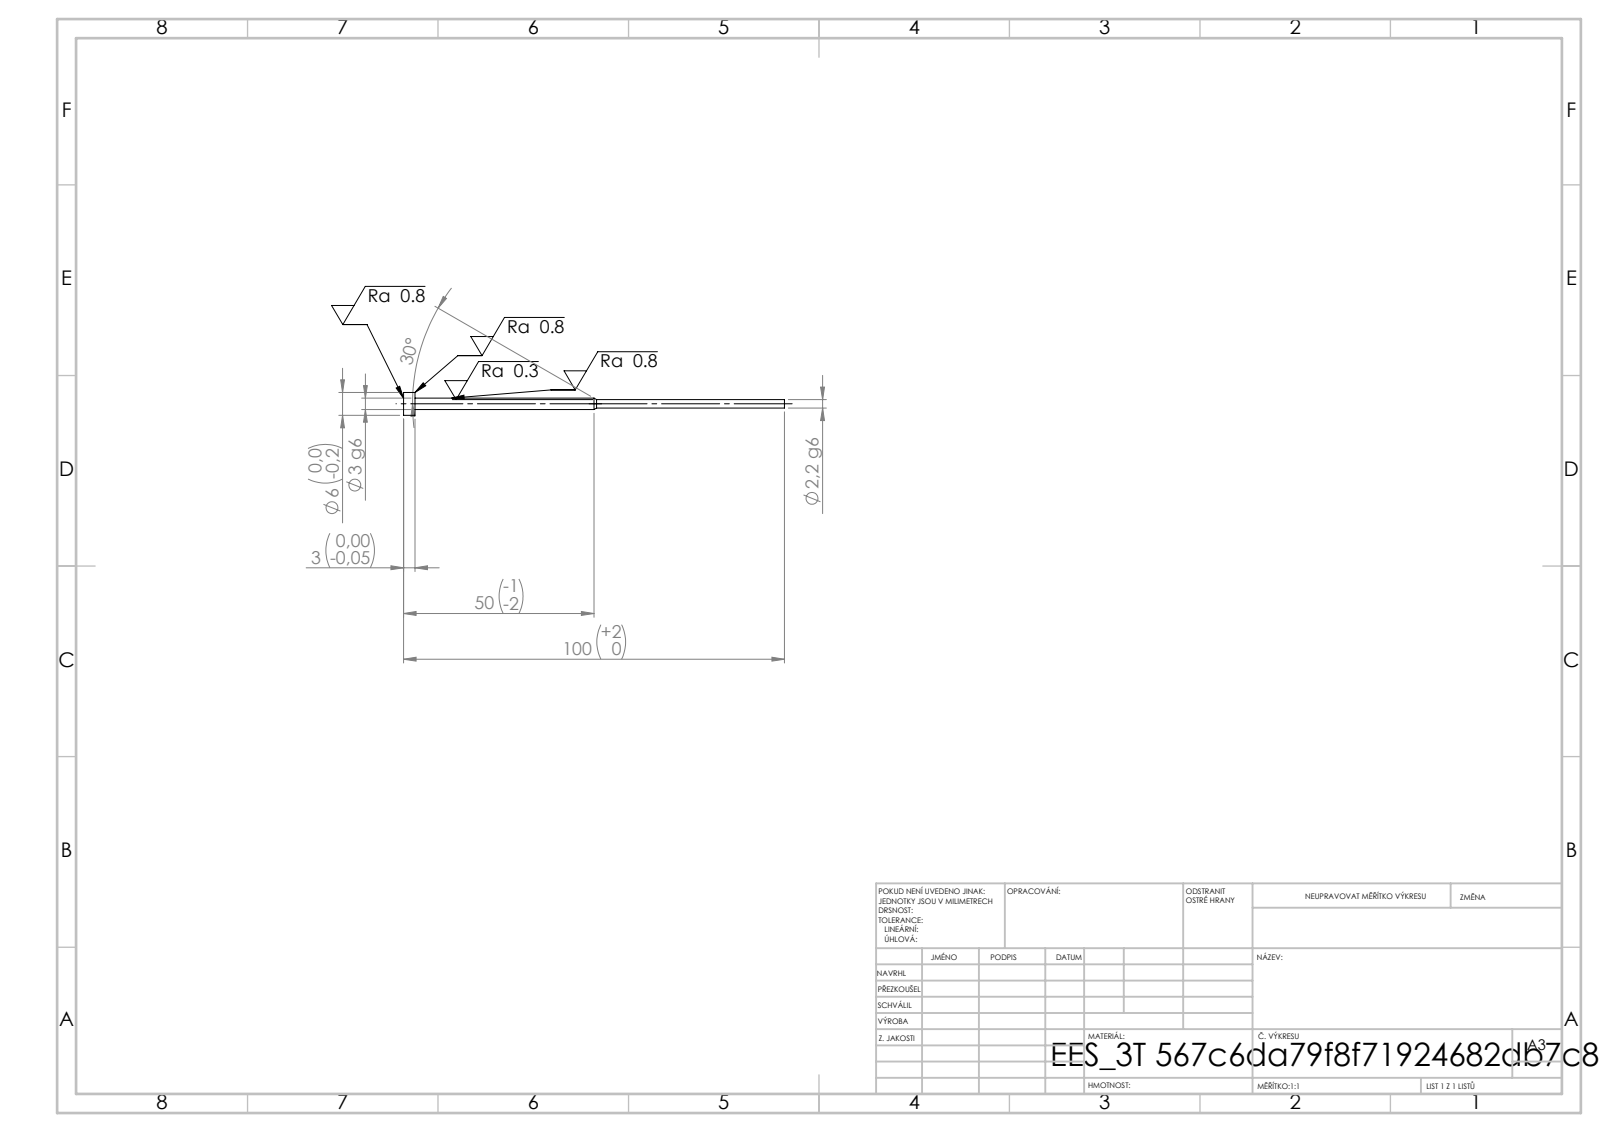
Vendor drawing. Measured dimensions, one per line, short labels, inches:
written by: SolidWorks 2019 (CONFIG_CONTROL_DESIGN)
unit: in
bodies: 1 solid, 11 faces (3 planar, 6 cylindrical, 2 other)
size: 3.937 × 0.236 × 0.236
volume: 0.037 in³; area: 1.4 in²
bosses: 1× ⌀0.236, 1× ⌀0.118, 1× ⌀0.087
face distances: 0.118, 3.819, 3.937
